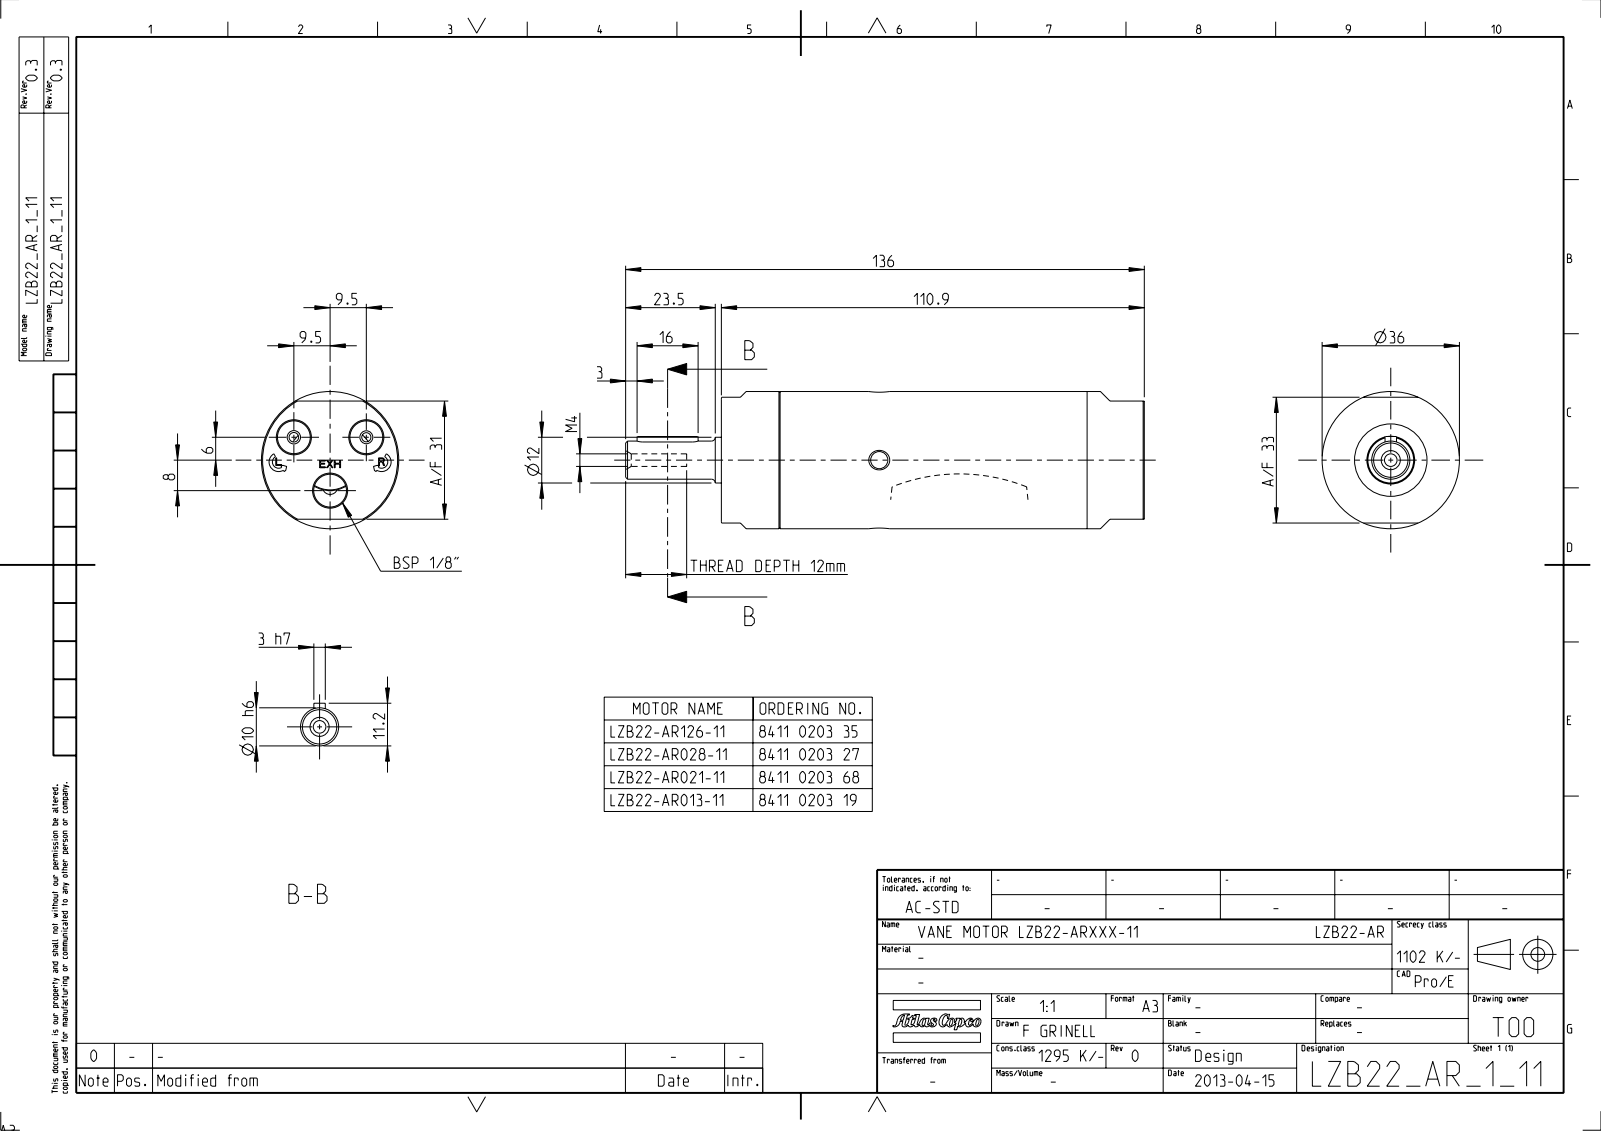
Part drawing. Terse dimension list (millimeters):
name: 4110106400; 4110107600; 4110106700; 4110106780_ASM (+4 more)
written by: CREO PARAMETRIC BY PTC INC, 2015080 (CONFIG_CONTROL_DESIGN)
unit: mm
bodies: 6 solids, 316 faces (145 planar, 98 cylindrical, 73 other)
size: 136 × 36 × 36
volume: 48 848 mm³; area: 36 015 mm²
holes: 3× ⌀8.6, 2× ⌀2.4, 2× ⌀3, 2× ⌀4.5, 1× ⌀2.5, 1× ⌀3.3, 1× ⌀4, 1× ⌀9.5, 1× ⌀15, 1× ⌀19, 1× ⌀20, 1× ⌀28
bosses: 1× ⌀36, 1× ⌀32, 1× ⌀25, 1× ⌀22.5, 1× ⌀12, 1× ⌀10
rounds: 4× R0.1, 2× R1.5, 2× R1.52, 2× R1.62, 2× R2.5, 2× R31.5, 1× R5, 1× R8.5
face distances: 110.9, 15, 95.9, 10.25, 3.25, 95.5, 80.5, 15.4, 3.5, 7
hole spacings: 17.58, 8.79, 9.9, 11.24, 13.09, 16.92, 0.79, 3
